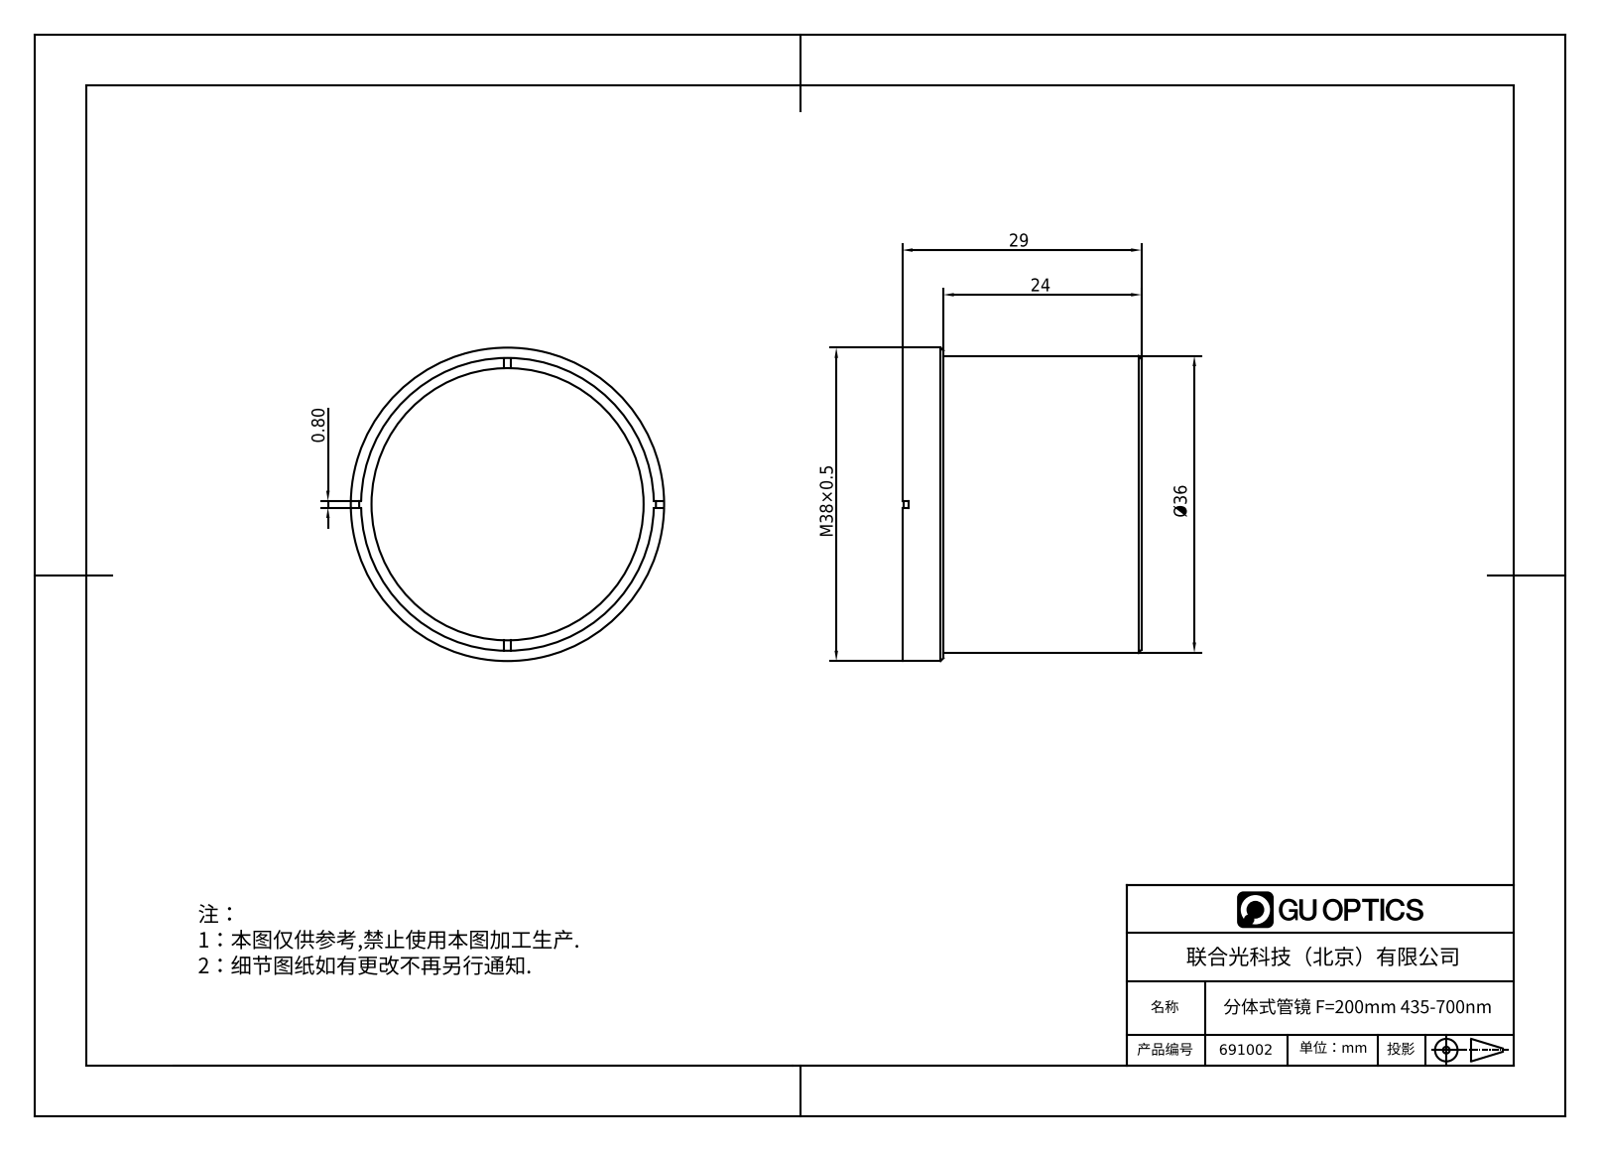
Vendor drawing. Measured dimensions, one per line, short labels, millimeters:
name: 691002; surfaces 5,6; 镜筒^f200round175_f_round; surfaces 3,4 (+4 more)
written by: SolidWorks 2020 (CONFIG_CONTROL_DESIGN)
unit: mm
bodies: 7 solids, 51 faces (26 planar, 14 cylindrical, 11 other)
size: 38 × 38 × 29
volume: 20 276 mm³; area: 19 175 mm²
holes: 1× ⌀29, 1× ⌀32.4, 1× ⌀33, 1× ⌀35.5, 1× ⌀36.5
bosses: 1× ⌀38, 1× ⌀36, 1× ⌀34
face distances: 1, 28, 1.13, 25.12, 25.25, 26.25, 1.75, 26.87, 27, 2.75
